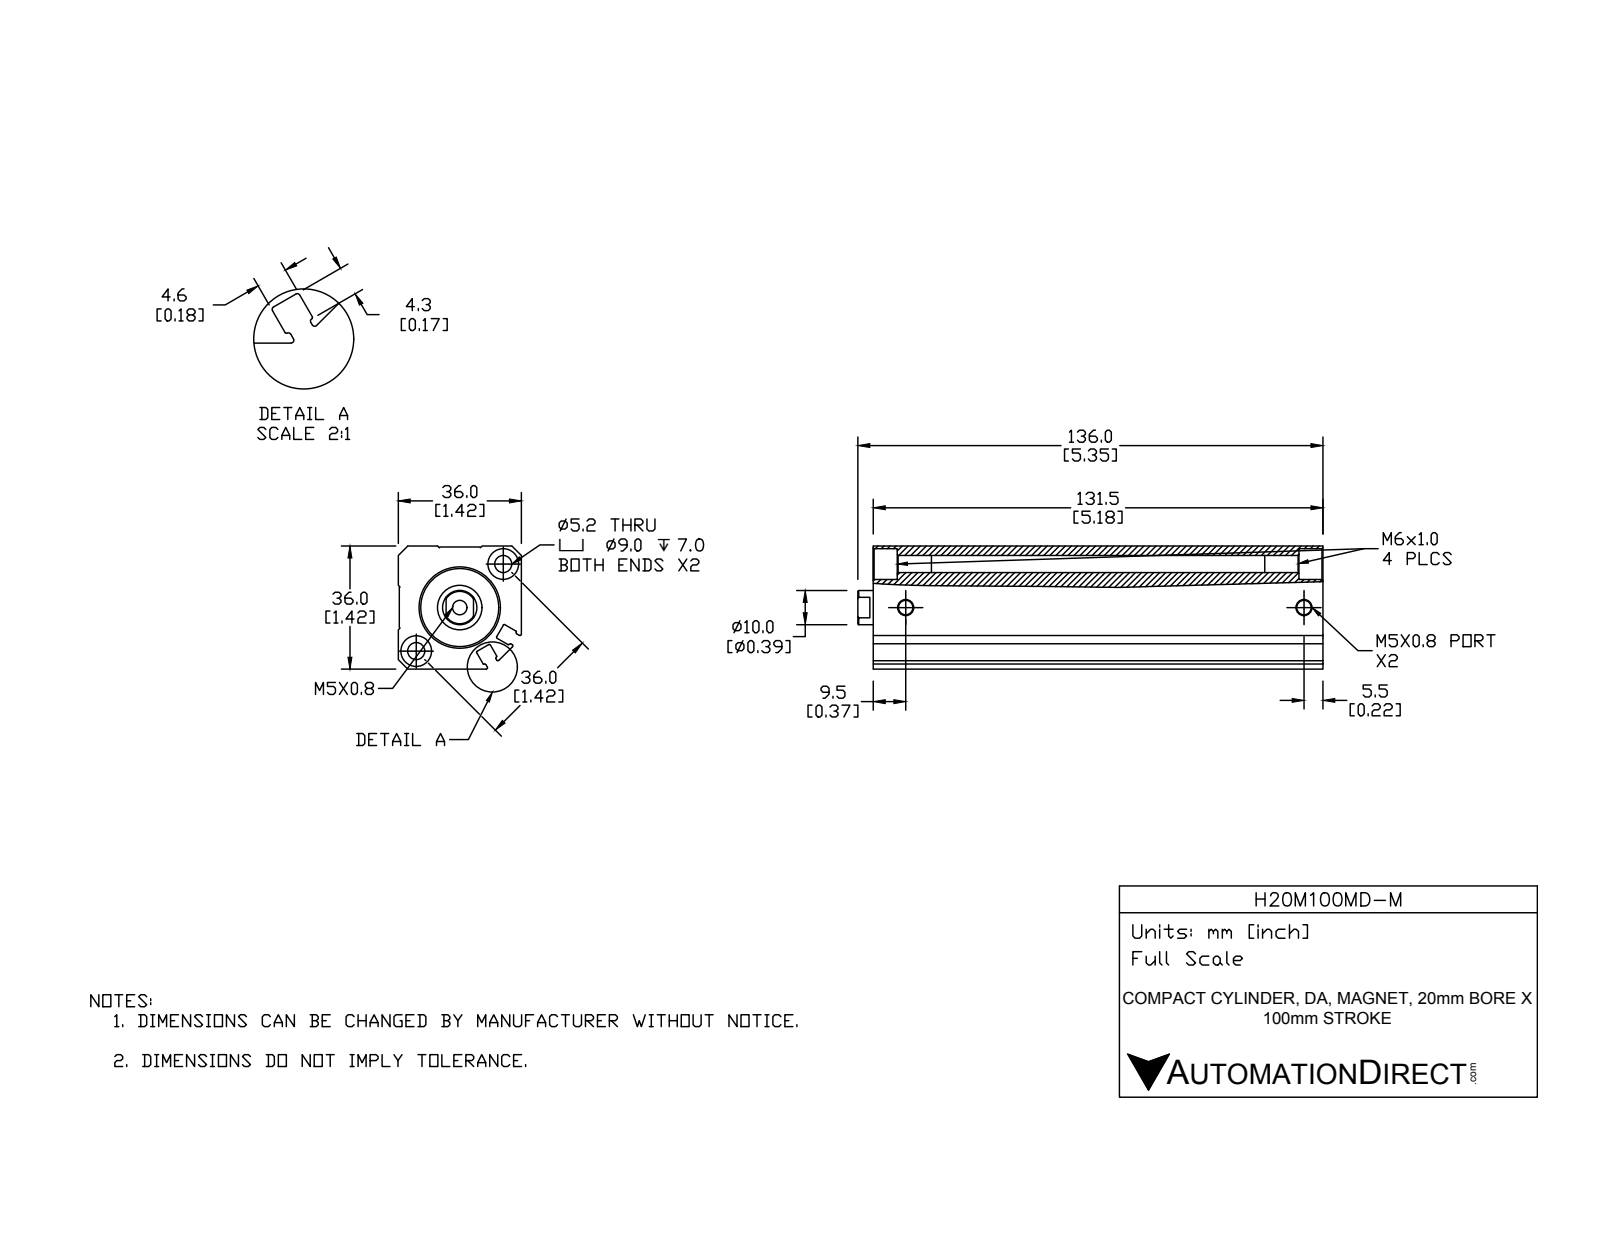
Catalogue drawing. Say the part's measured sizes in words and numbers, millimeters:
The part is named "H20M100MD-M-BODY; H20M100MD-M-PISTON; H20M100MD-M". Its 3-D file was written by "SolidWorks 2015 (CONFIG_CONTROL_DESIGN)". It is 2 solids with 141 faces: 53 planar, 55 cylindrical and 33 other. Overall it measures 136 by 36 by 36 millimeters. Its volume is 124 417 cubic millimeters and its surface area 41 851 square millimeters. Round holes: 3 of diameter 4.2, 2 of diameter 5, 2 of diameter 9, 1 of diameter 10, 1 of diameter 13, 1 of diameter 20, 1 of diameter 22.8. Round bosses or shafts: 1 of diameter 11. Partial cylindrical surfaces (rounded edges, fillets, slot ends): 12 of radius 0.4, 4 of radius 0.2. The main face-to-face distances are 36, 35.7, 4.6, 4, 131.5, 127.5, 46.98, 2.6, 15.36, 0.6. The hole center spacings are 18, 36.01, 116.5.
